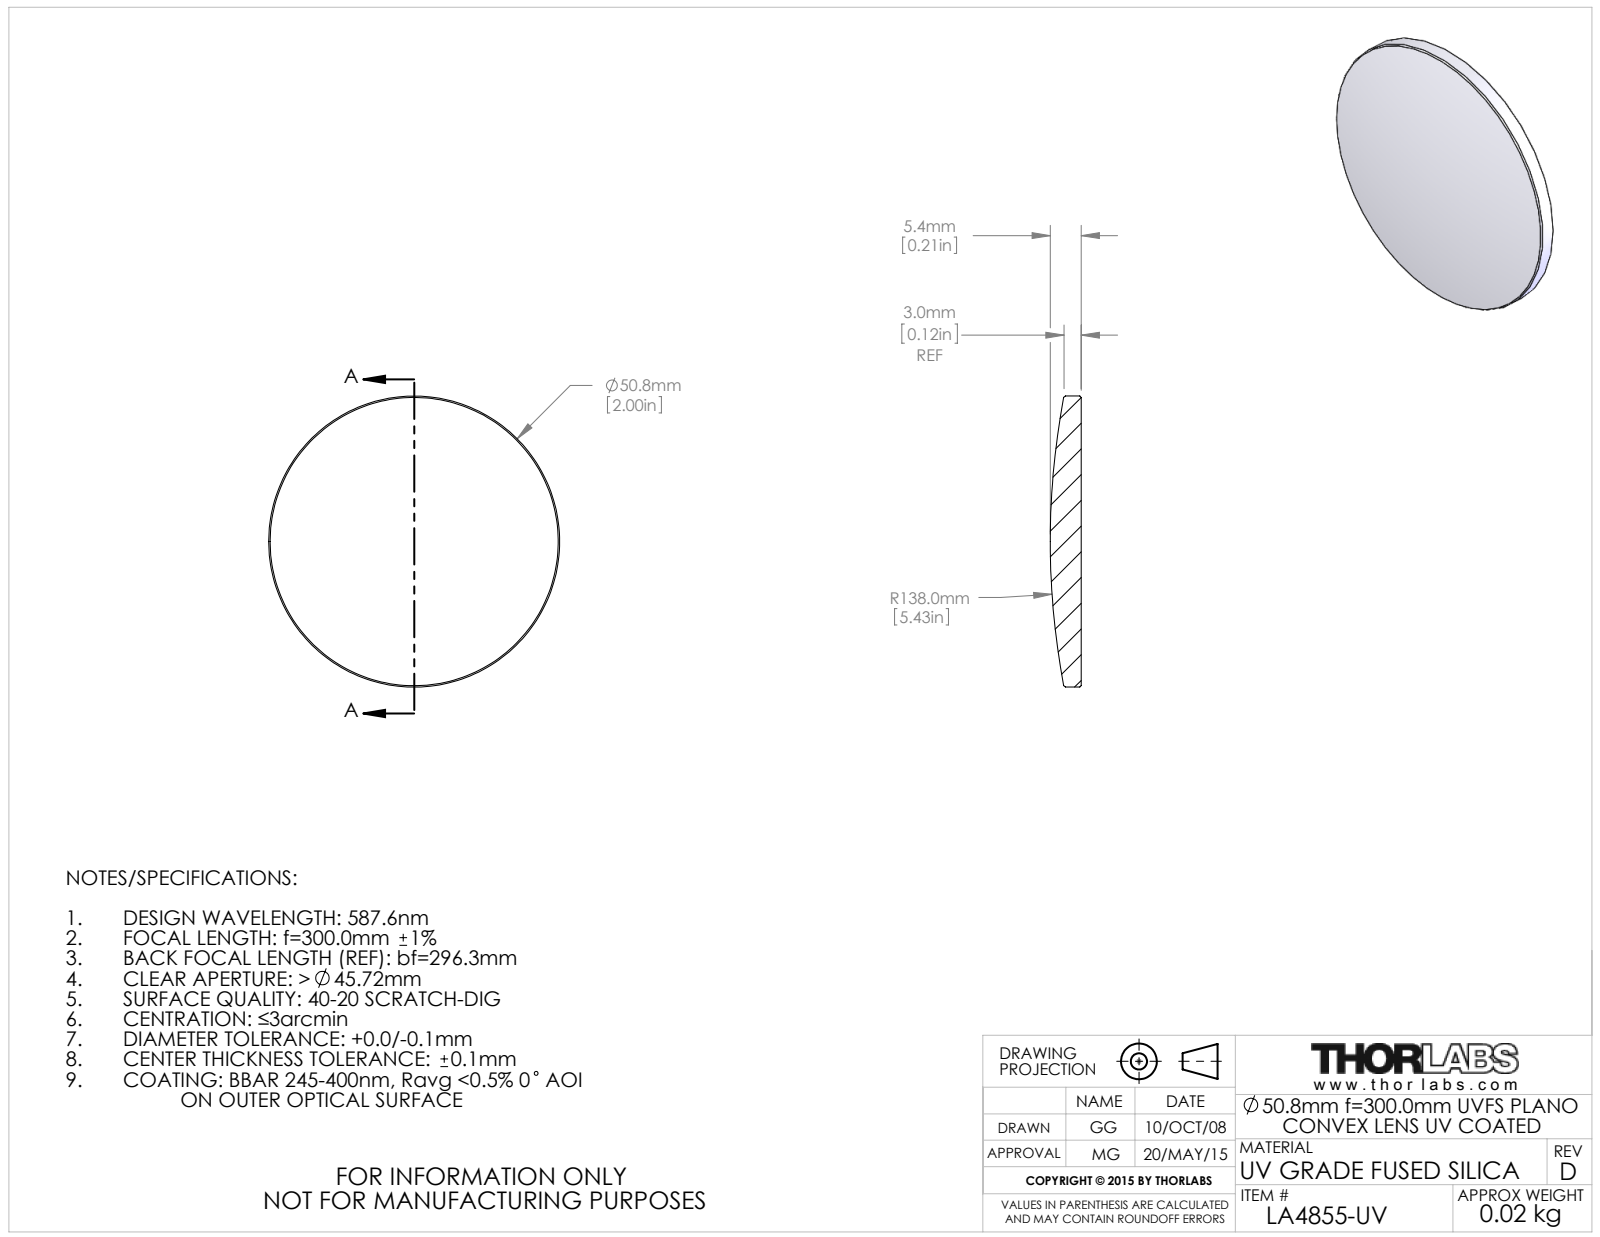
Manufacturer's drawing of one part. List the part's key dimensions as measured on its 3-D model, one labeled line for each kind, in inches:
Part name (STEP PRODUCT): 4298-E0W
STEP written by: SolidWorks 2014 (CONFIG_CONTROL_DESIGN)
Units: inches
Bodies: 1 solid, 9 faces (1 planar, 2 cylindrical, 6 other)
Overall size (bounding box): 2 × 2 × 0.213
Volume: 0.518 in³ · Surface area: 6.987 in²
Round bosses / shafts (diameter × count): ⌀2 ×1
